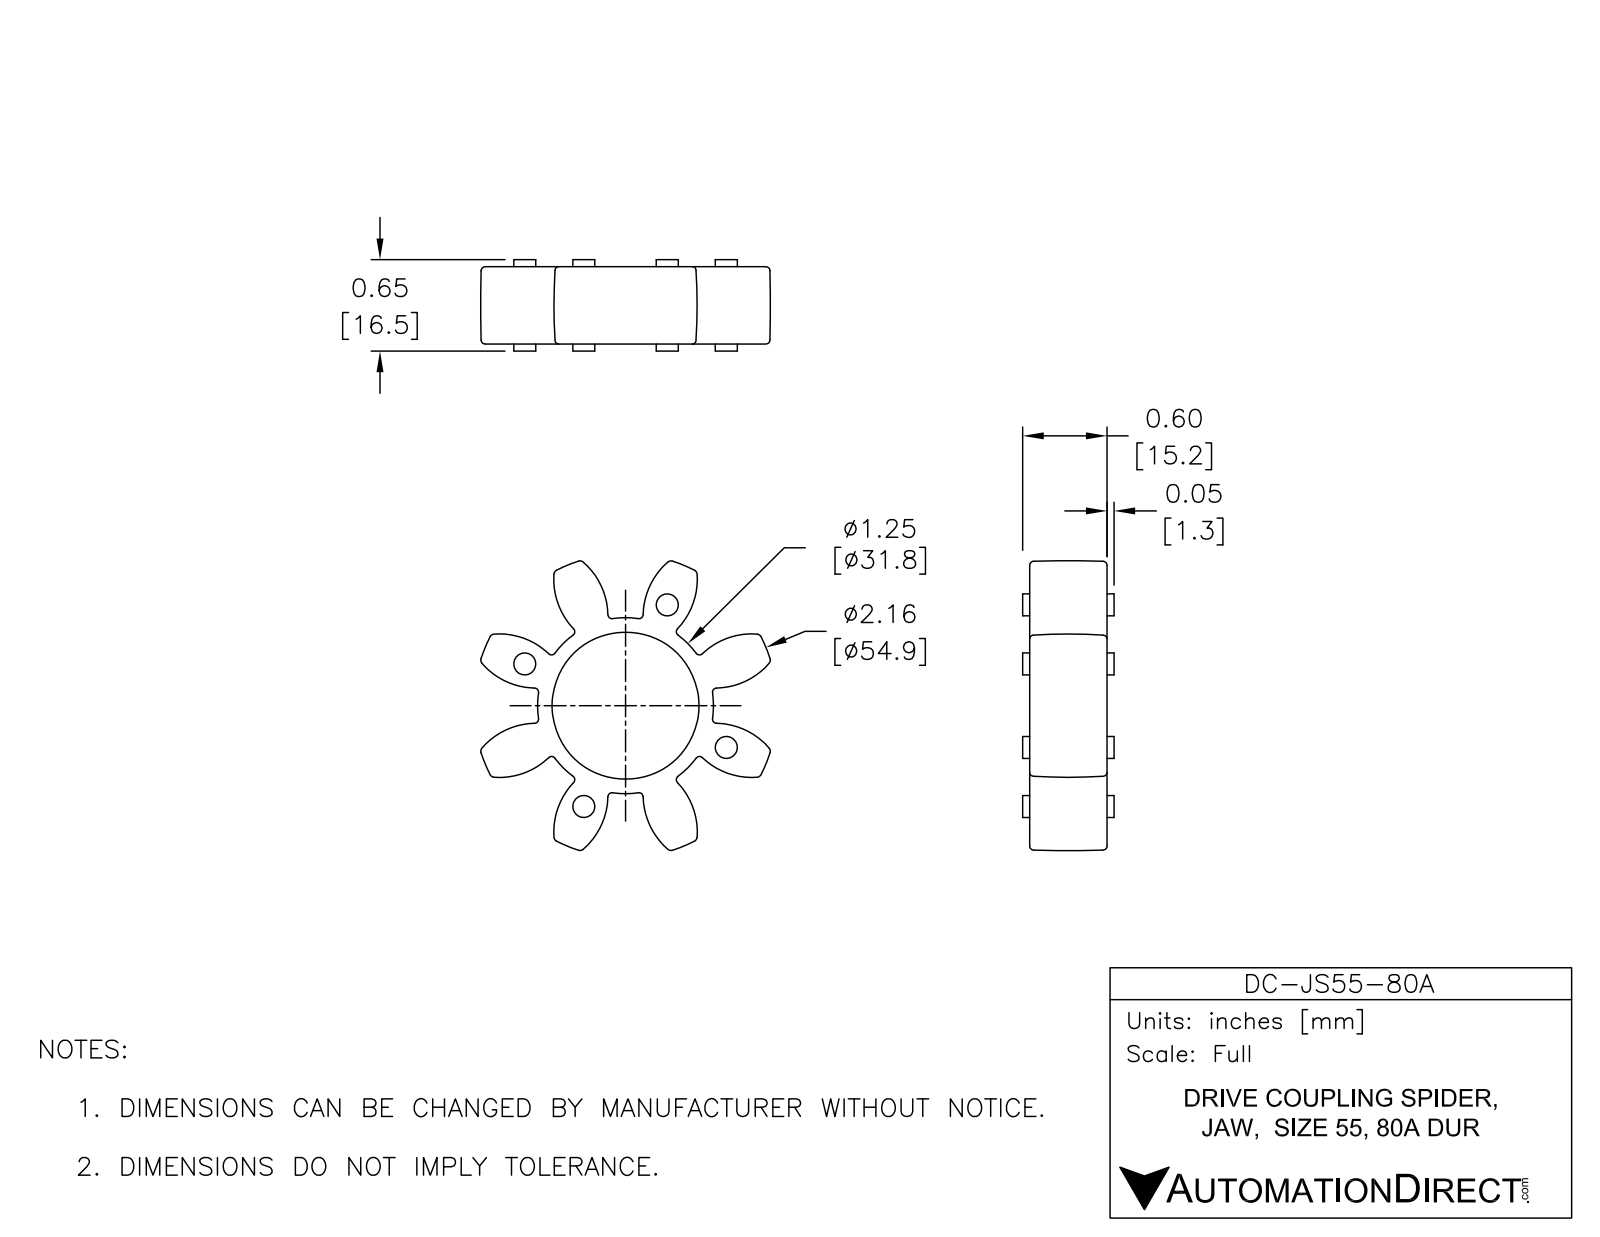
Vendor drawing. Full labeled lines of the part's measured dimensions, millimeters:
Part name (STEP PRODUCT): DC-JS55-80A
STEP written by: SolidWorks 2015 (AUTOMOTIVE_DESIGN)
Units: millimetres
Bodies: 1 solid, 258 faces (10 planar, 56 cylindrical, 192 other)
Overall size (bounding box): 52.11 × 52.11 × 16.51
Volume: 12 424 mm³ · Surface area: 6 712 mm²
Round holes (diameter × count): ⌀26.54 ×1
Round bosses / shafts (diameter × count): ⌀3.96 ×8
Partial cylindrical surfaces — rounded edges, fillets, slot ends (radius × count): R0.75 ×32
Main face-to-face distances: 13.98, 1.27, 15.25, 16.52
